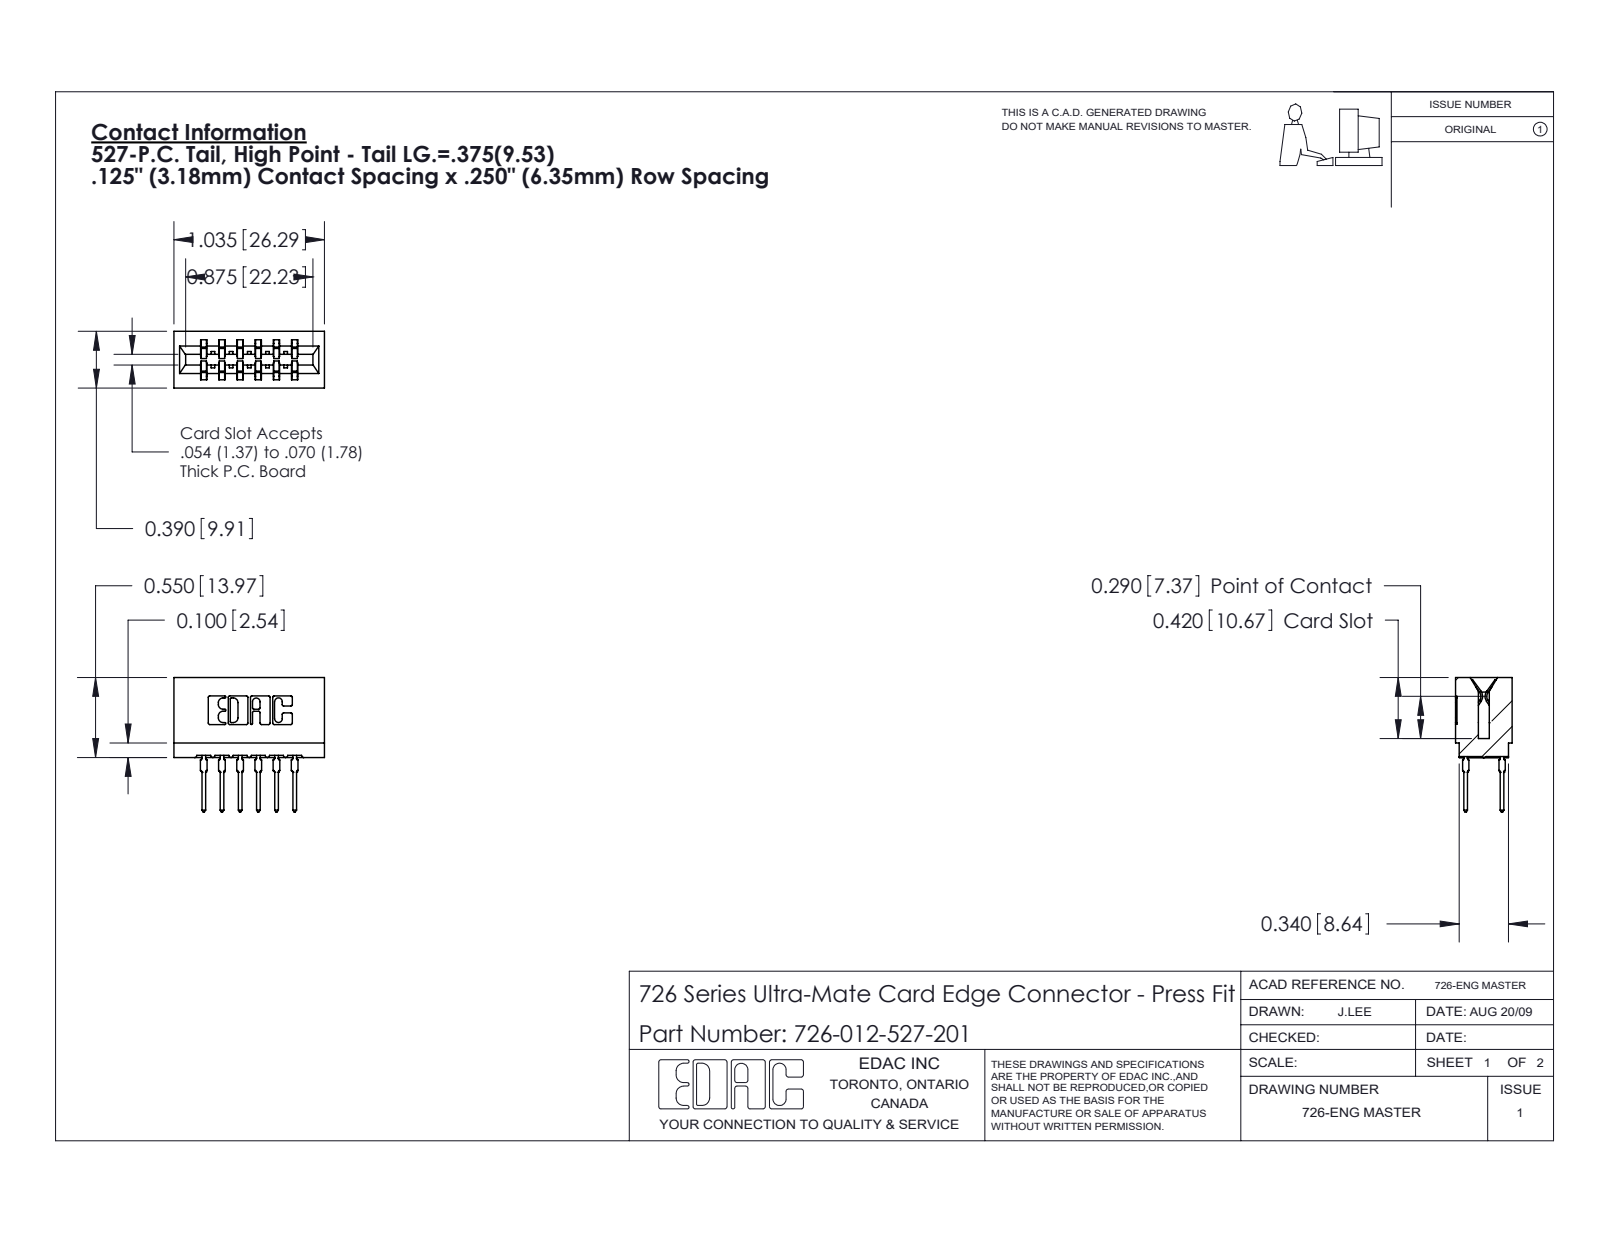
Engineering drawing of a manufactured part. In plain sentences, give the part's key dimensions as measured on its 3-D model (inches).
The part is named "726 Part_.515 Slot Depth - 01; 726-012-527-201; 746-292-001_527". Its 3-D file was written by "SolidWorks 2020 (CONFIG_CONTROL_DESIGN)". It is 13 solids with 1171 faces: 607 planar, 252 cylindrical and 312 other. Overall it measures 1.035 by 0.924 by 0.39 inches. Its volume is 0.16 cubic inches and its surface area 5.949 square inches. Partial cylindrical surfaces (rounded edges, fillets, slot ends): 24 of radius 0.021, 22 of radius 0.01, 8 of radius 0.005, 8 of radius 0.011, 7 of radius 0.015, 6 of radius 0.007, 6 of radius 0.031, 3 of radius 0.026. The main face-to-face distances are 0.25, 0.057, 0.125, 0.333, 0.042, 0.375, 0.025, 0.083, 0.307, 0.125.
